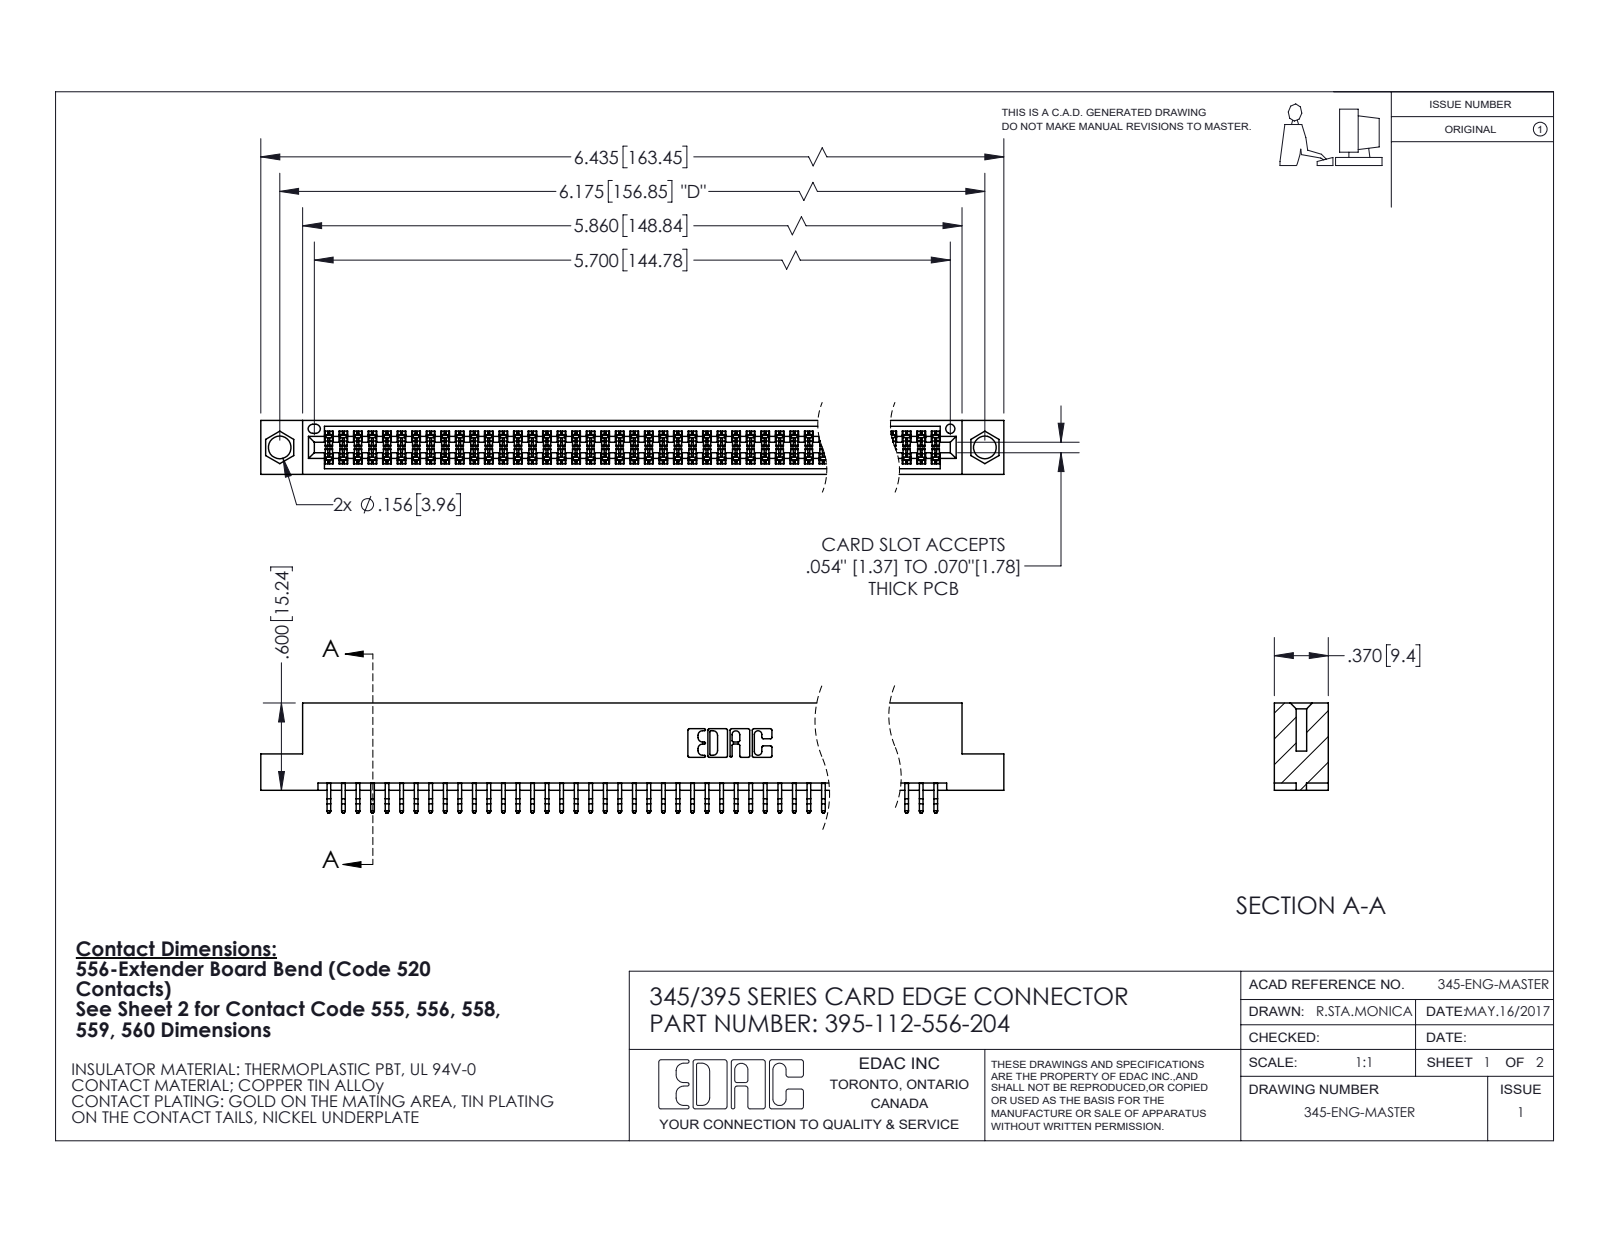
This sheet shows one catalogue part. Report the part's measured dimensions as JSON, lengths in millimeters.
{"part_name": "345-292-001_556 Tail; 395-112-556-204; 345 Part_Flush Mounting Lugs - 0.156 Dia-TI", "step_written_by": "SolidWorks 2020 (CONFIG_CONTROL_DESIGN)", "units": "millimeters", "bodies": {"solids": 113, "faces": 6412, "planar": 4238, "cylindrical": 2174, "other": 0}, "overall_size": [163.4, 19.2, 9.4], "volume_mm3": 15900, "surface_area_mm2": 23520, "round_holes": [[4, 2], [1.6, 1]], "partial_cylinders_radius": [[0.2, 224], [0.3, 22], [0.2, 6], [0.8, 6], [0.7, 3], [0.3, 2], [0.4, 2], [0.5, 2]], "face_to_face_distances": [7.6, 1.8, 9.4, 5.1, 0.6, 2.5, 6.9, 5.7, 4.4, 3.8], "hole_center_spacings": [6.9, 150.9, 156.8]}
